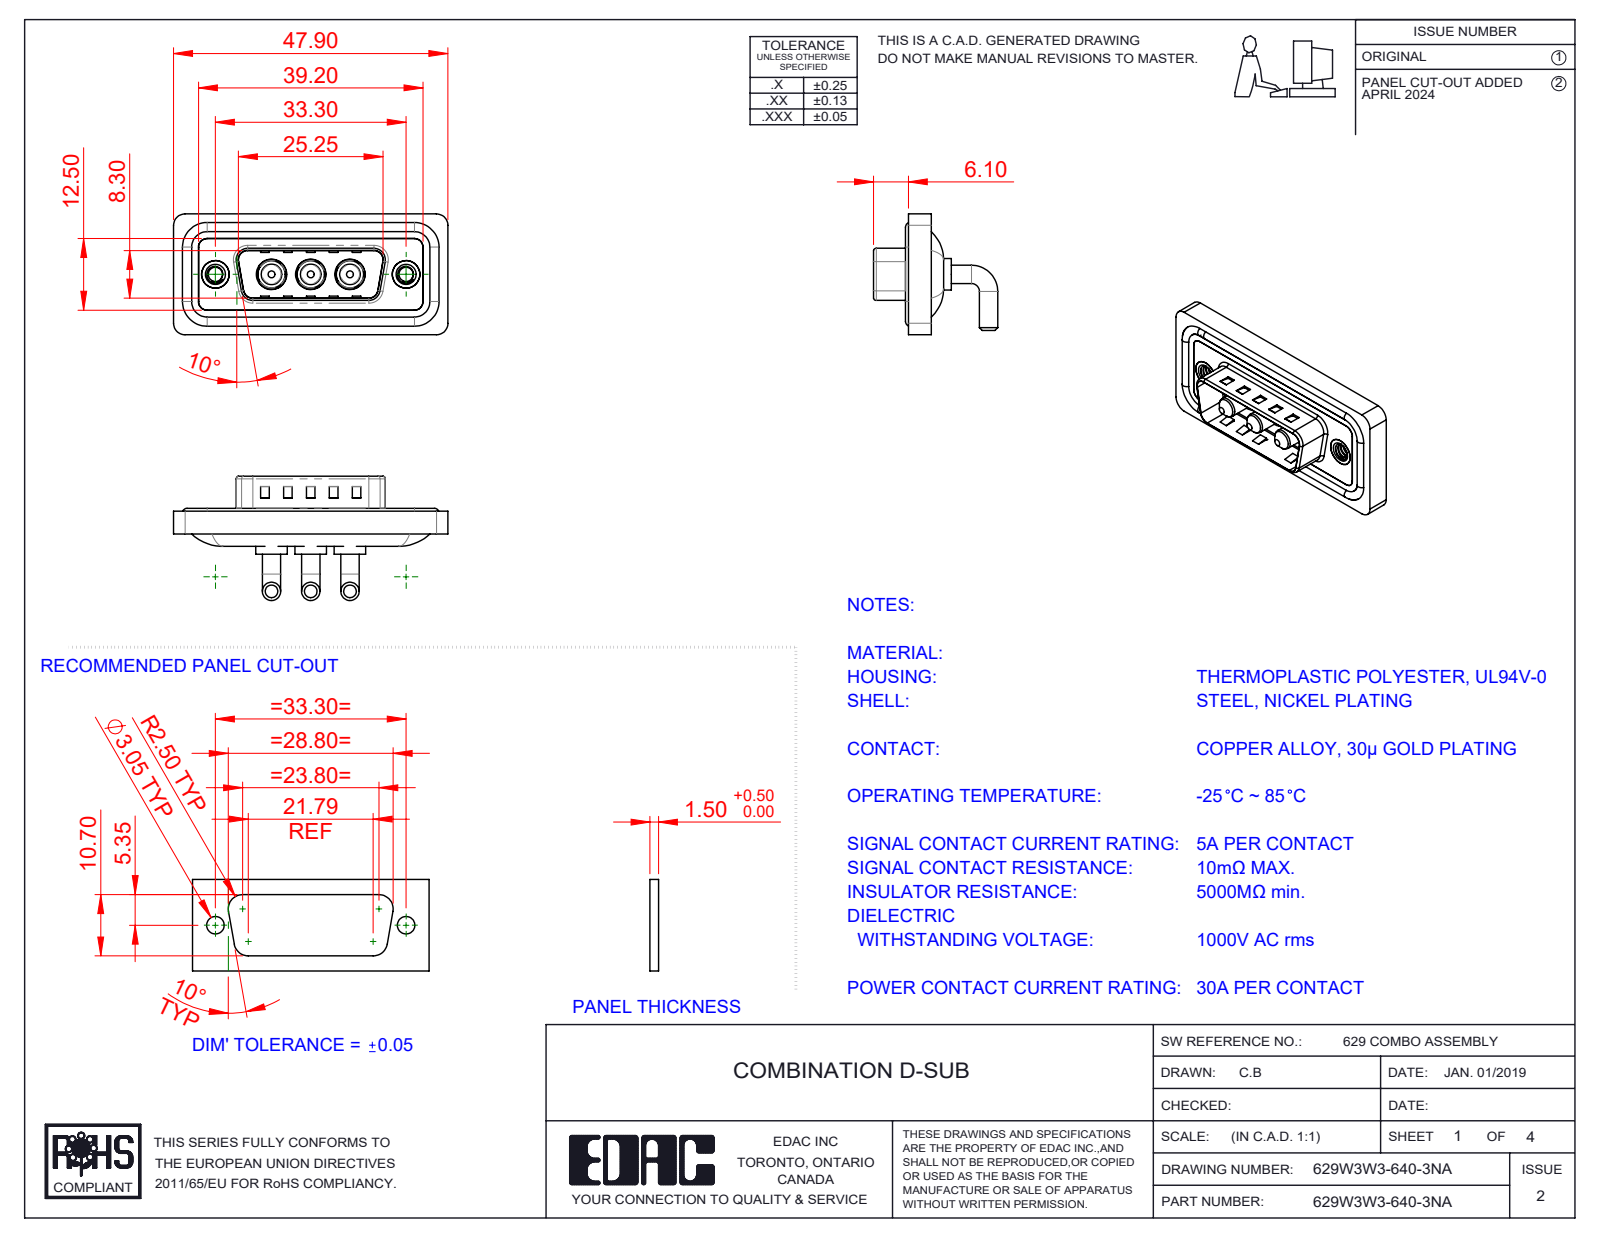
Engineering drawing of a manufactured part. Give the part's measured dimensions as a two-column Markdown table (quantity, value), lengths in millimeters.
| quantity | value |
| --- | --- |
| part name | 629Combo Waterproof Housing_15 Contacts; 629Combo Shell Rear_15 Contacts; 629W3W3-640-3NA; 629Combo Threaded Rivet_A (+3 more) |
| STEP written by | SolidWorks 2023 (CONFIG_CONTROL_DESIGN) |
| units | millimeters |
| bodies | 13 solids, 570 faces (207 planar, 245 cylindrical, 118 other) |
| overall size | 47.9 × 21.7 × 21.1 |
| volume | 5 866 mm³ |
| surface area | 9 095 mm² |
| round holes (diameter × count) | 4.85 × 3, 5.3 × 3, 2.5 × 2, 4 × 2, 4.8 × 2, 5 × 2 |
| round bosses / shafts (diameter × count) | 3.2 × 6, 1.6 × 4, 5.5 × 3, 5.2 × 3, 4.75 × 3, 3.75 × 3, 3.6 × 3, 4.9 × 2 |
| partial cylindrical surfaces (radius × count) | 2 × 20, 1.5 × 18, 0.5 × 8, 1.6 × 8, 0.25 × 4, 0.6 × 4, 0.65 × 4, 0.9 × 4 |
| main face-to-face distances | 0.4, 2.9, 0.8, 1.1, 2.1, 1.6, 3.1, 2.5, 4.5, 3.7 |
| hole center spacings | 6.85, 9.8, 16.65, 23.5, 13.7, 33.3 |
